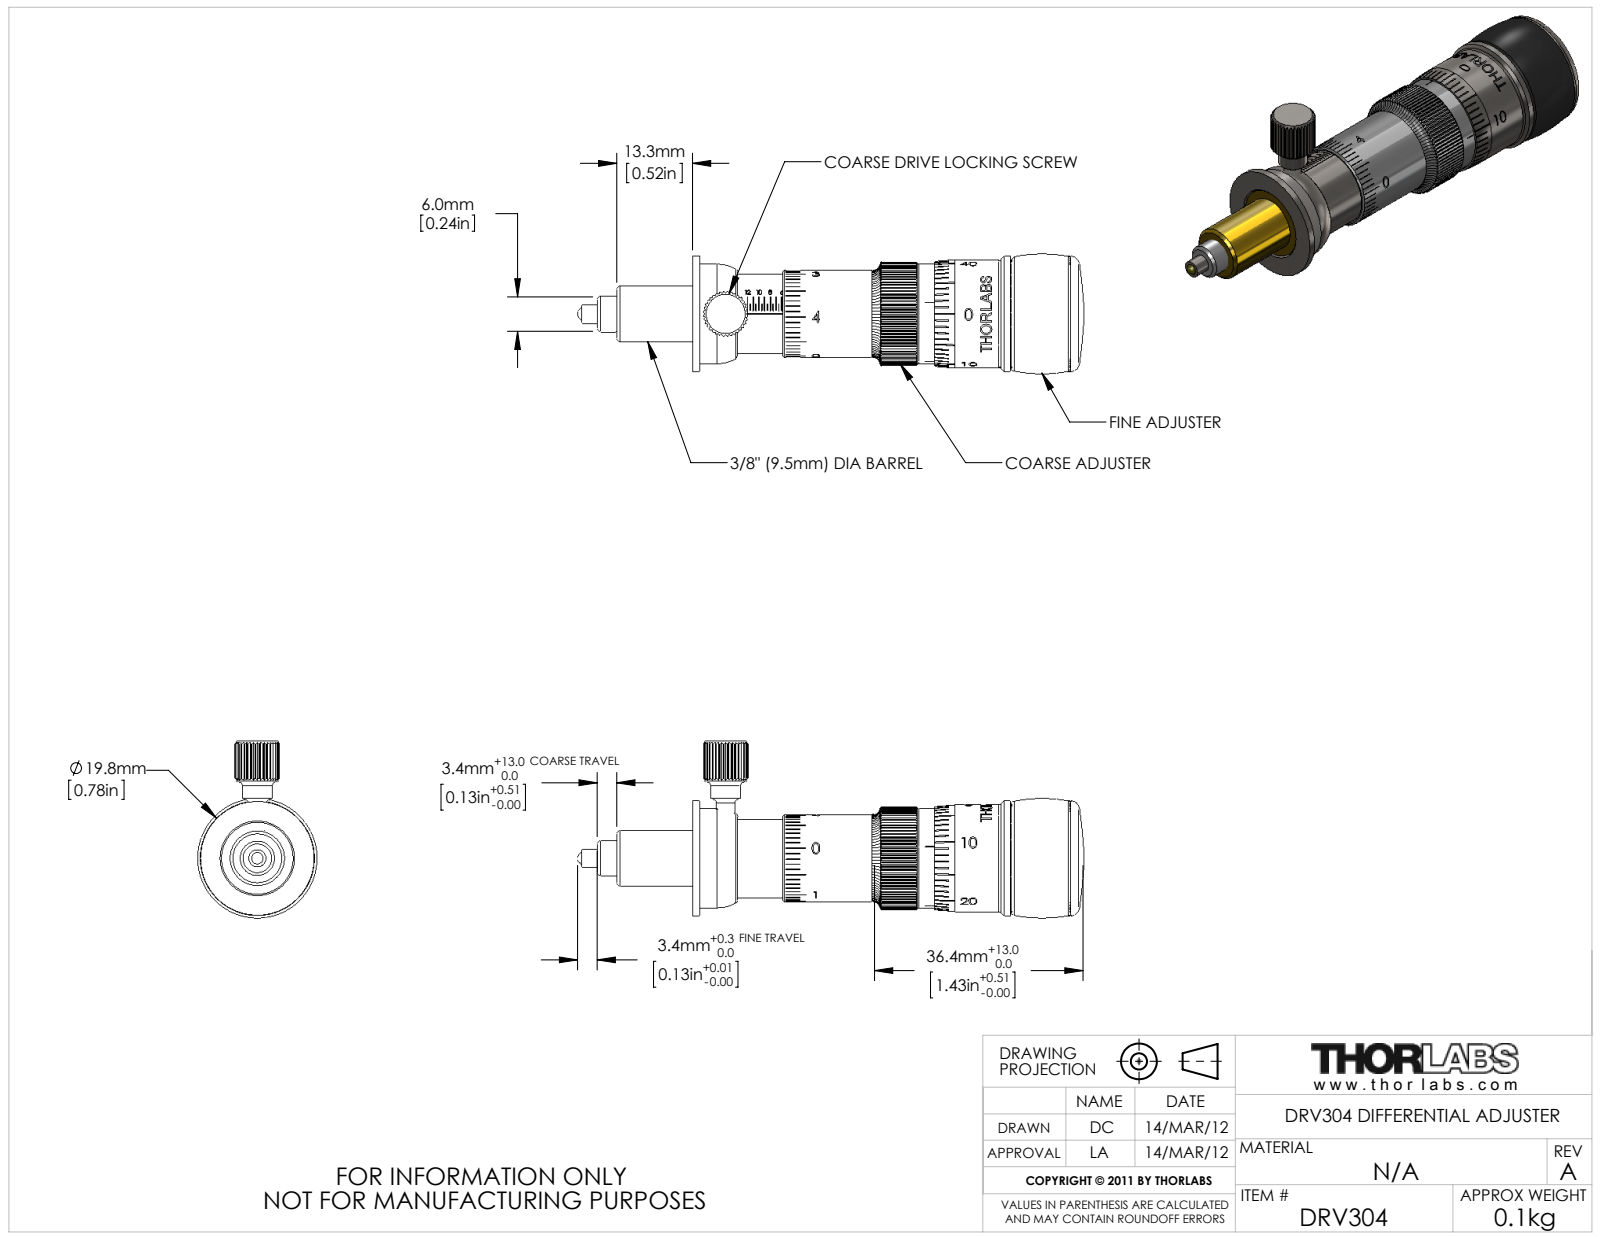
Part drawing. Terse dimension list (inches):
name: DRV304 - Coarse Scale
written by: SolidWorks 2011 (AUTOMOTIVE_DESIGN)
unit: in
bodies: 33 solids, 2156 faces (849 planar, 551 cylindrical, 756 other)
size: 3.464 × 1.294 × 0.983
volume: 0.93 in³; area: 28.96 in²
holes: 5× ⌀0.039, 4× ⌀0.063, 3× ⌀0.049, 2× ⌀0.098, 1× ⌀0.079, 1× ⌀0.091, 1× ⌀0.126, 1× ⌀0.173, 1× ⌀0.197, 1× ⌀0.217, 1× ⌀0.346, 1× ⌀0.354
bosses: 4× ⌀0.059, 3× ⌀0.118, 1× ⌀0.78, 1× ⌀0.724, 1× ⌀0.669, 1× ⌀0.614, 1× ⌀0.591, 1× ⌀0.545
rounds: 12× R0.02, 8× R0.004, 1× R0.03, 1× R0.043, 1× R0.054, 1× R0.081, 1× R0.154, 1× R0.258
face distances: 0.047, 0.098, 1.275, 0.051, 1.228, 1.177, 0.039, 0.079, 2.4, 2.353
hole spacings: 0.161, 0.374, 0.378, 0.539, 0.752, 0.913, 1.341, 1.715
